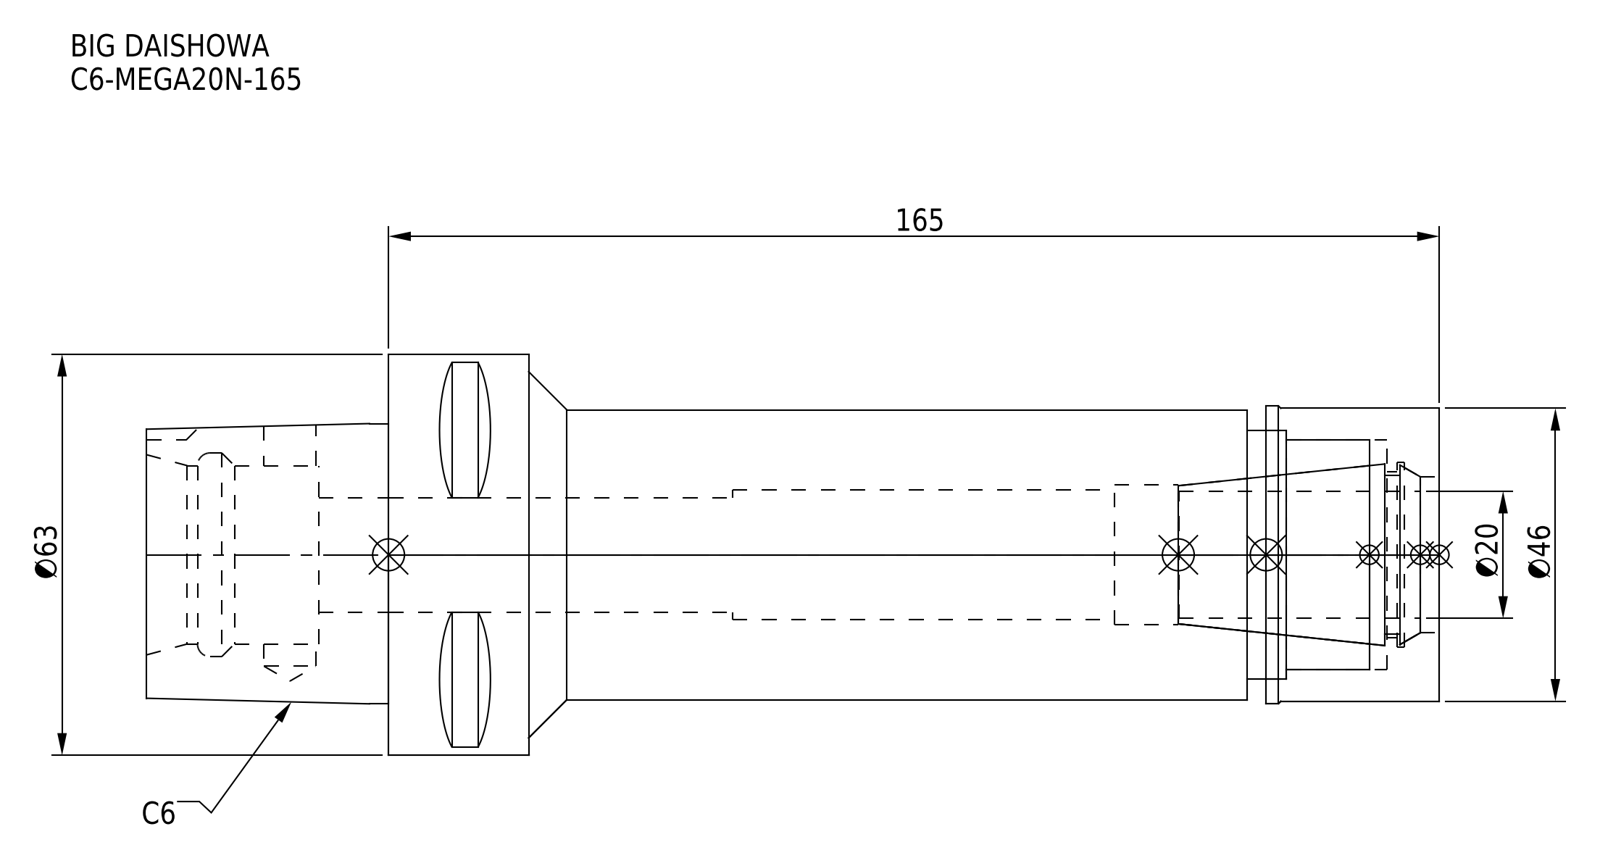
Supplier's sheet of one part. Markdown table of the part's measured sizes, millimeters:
| quantity | value |
| --- | --- |
| part name | C6-MEGA20N-165-200_ASM.stp; C6-MEGA20N-165-200.stp; C6-MEGA20N-165; DXF_TEMP_ASSY_ASM_4_ASM.stp (+3 more) |
| STEP written by | SolidWorks 2019 (CONFIG_CONTROL_DESIGN) |
| units | millimeters |
| bodies | 2 solids, 95 faces (38 planar, 39 cylindrical, 18 other) |
| overall size | 203 × 63 × 63 |
| volume | 276 999 mm³ |
| surface area | 55 734 mm² |
| round holes (diameter × count) | 8.1 × 1, 18 × 1, 20.3 × 1, 22 × 1, 24.5 × 1, 26 × 1, 28 × 1, 29 × 1, 32 × 1, 36 × 1, 39 × 1 |
| round bosses / shafts (diameter × count) | 63 × 1, 46.7 × 1, 46 × 1, 45.5 × 1 |
| partial cylindrical surfaces (radius × count) | 5 × 1 |
| main face-to-face distances | 165, 22, 134.8, 11, 60, 143, 27.2, 115.8, 137.8, 203 |
